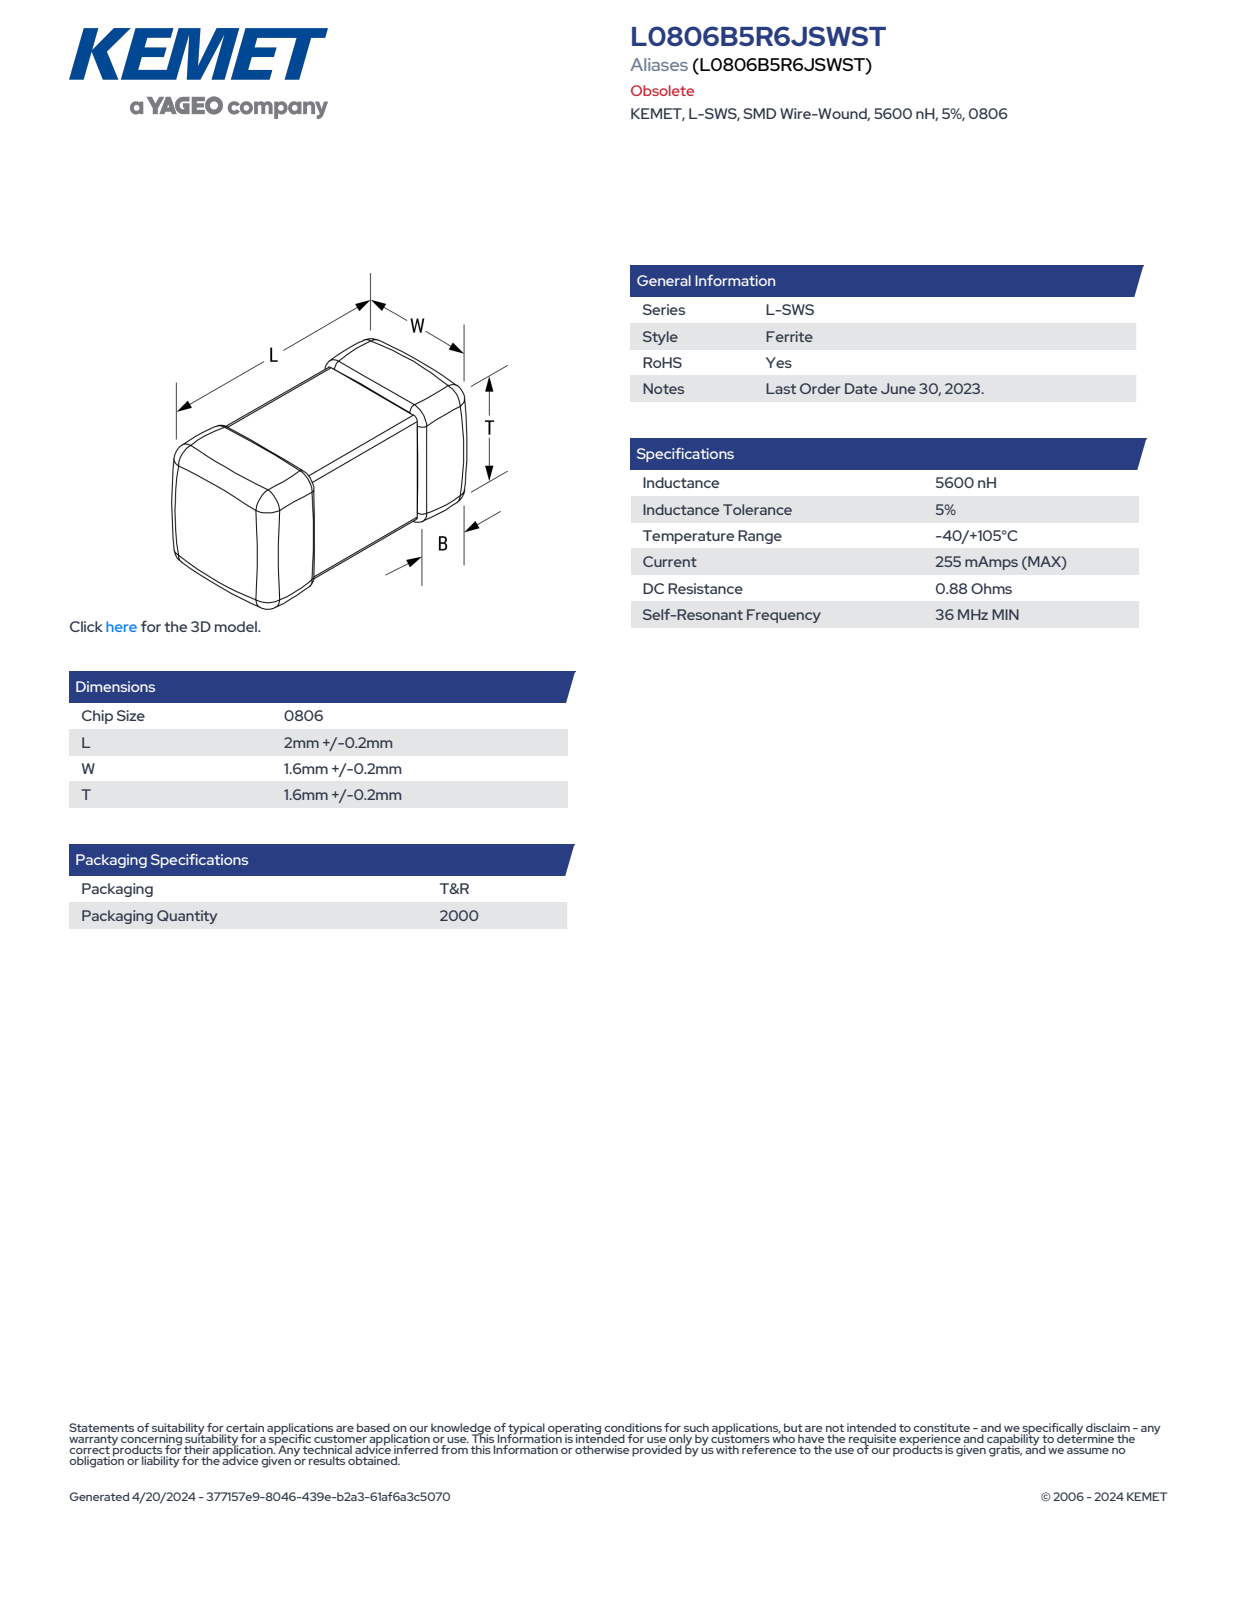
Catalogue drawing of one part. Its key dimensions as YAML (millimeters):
part_name: "IS_KC_0806_L2.2W1.8T1.8LL0.7"
step_written_by: "SolidWorks 2014 (AUTOMOTIVE_DESIGN)"
units: millimeters
bodies: {solids: 4, faces: 73, planar: 73, cylindrical: 0, other: 0}
overall_size: [2.2, 1.8, 1.8]
volume: 7
surface_area: 23
face_to_face_distances: [1.77, 1.8, 2.2, 1.74, 0.7, 1.5, 0.8, 1, 1.2, 0.5]
